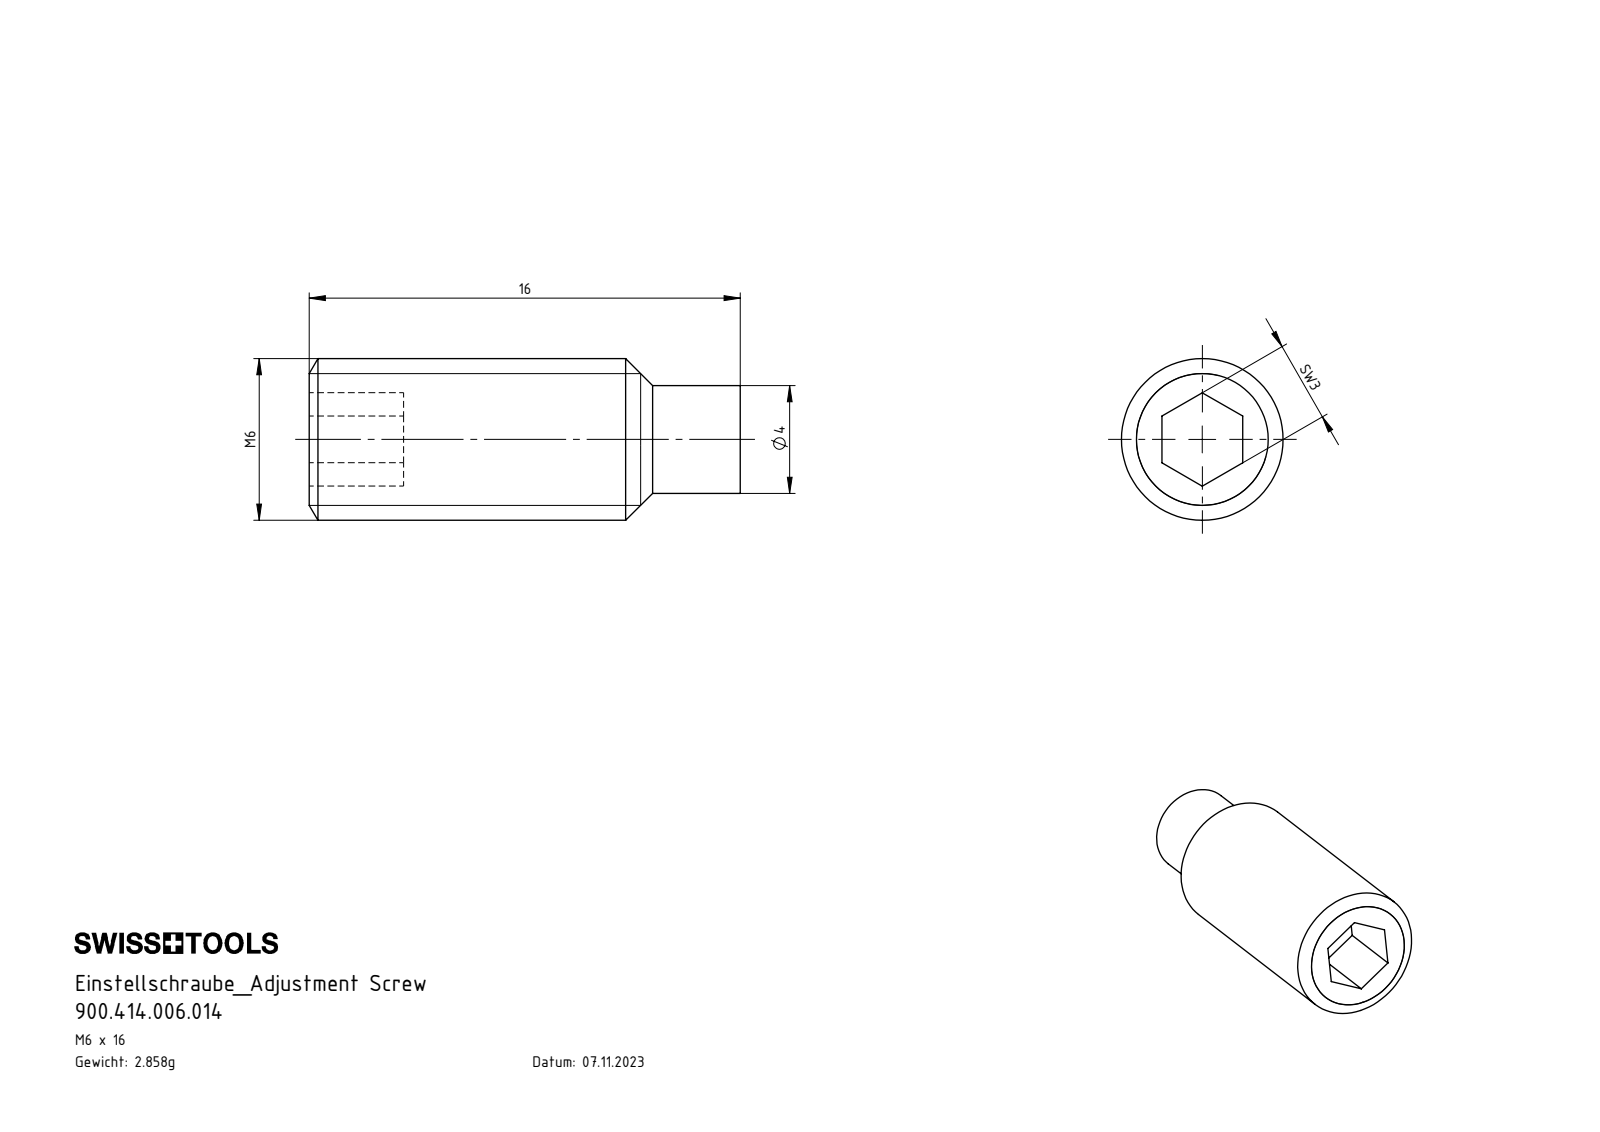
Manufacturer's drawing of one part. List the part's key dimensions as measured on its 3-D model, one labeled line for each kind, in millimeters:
Part name (STEP PRODUCT): 900.414.006.014
STEP written by: SolidWorks 2022 (AUTOMOTIVE_DESIGN)
Units: millimetres
Bodies: 1 solid, 17 faces (9 planar, 4 cylindrical, 4 other)
Overall size (bounding box): 16 × 6 × 6
Volume: 364 mm³ · Surface area: 357 mm²
Round bosses / shafts (diameter × count): ⌀6 ×1, ⌀4 ×1
Main face-to-face distances: 3, 16, 3.5, 12.5
